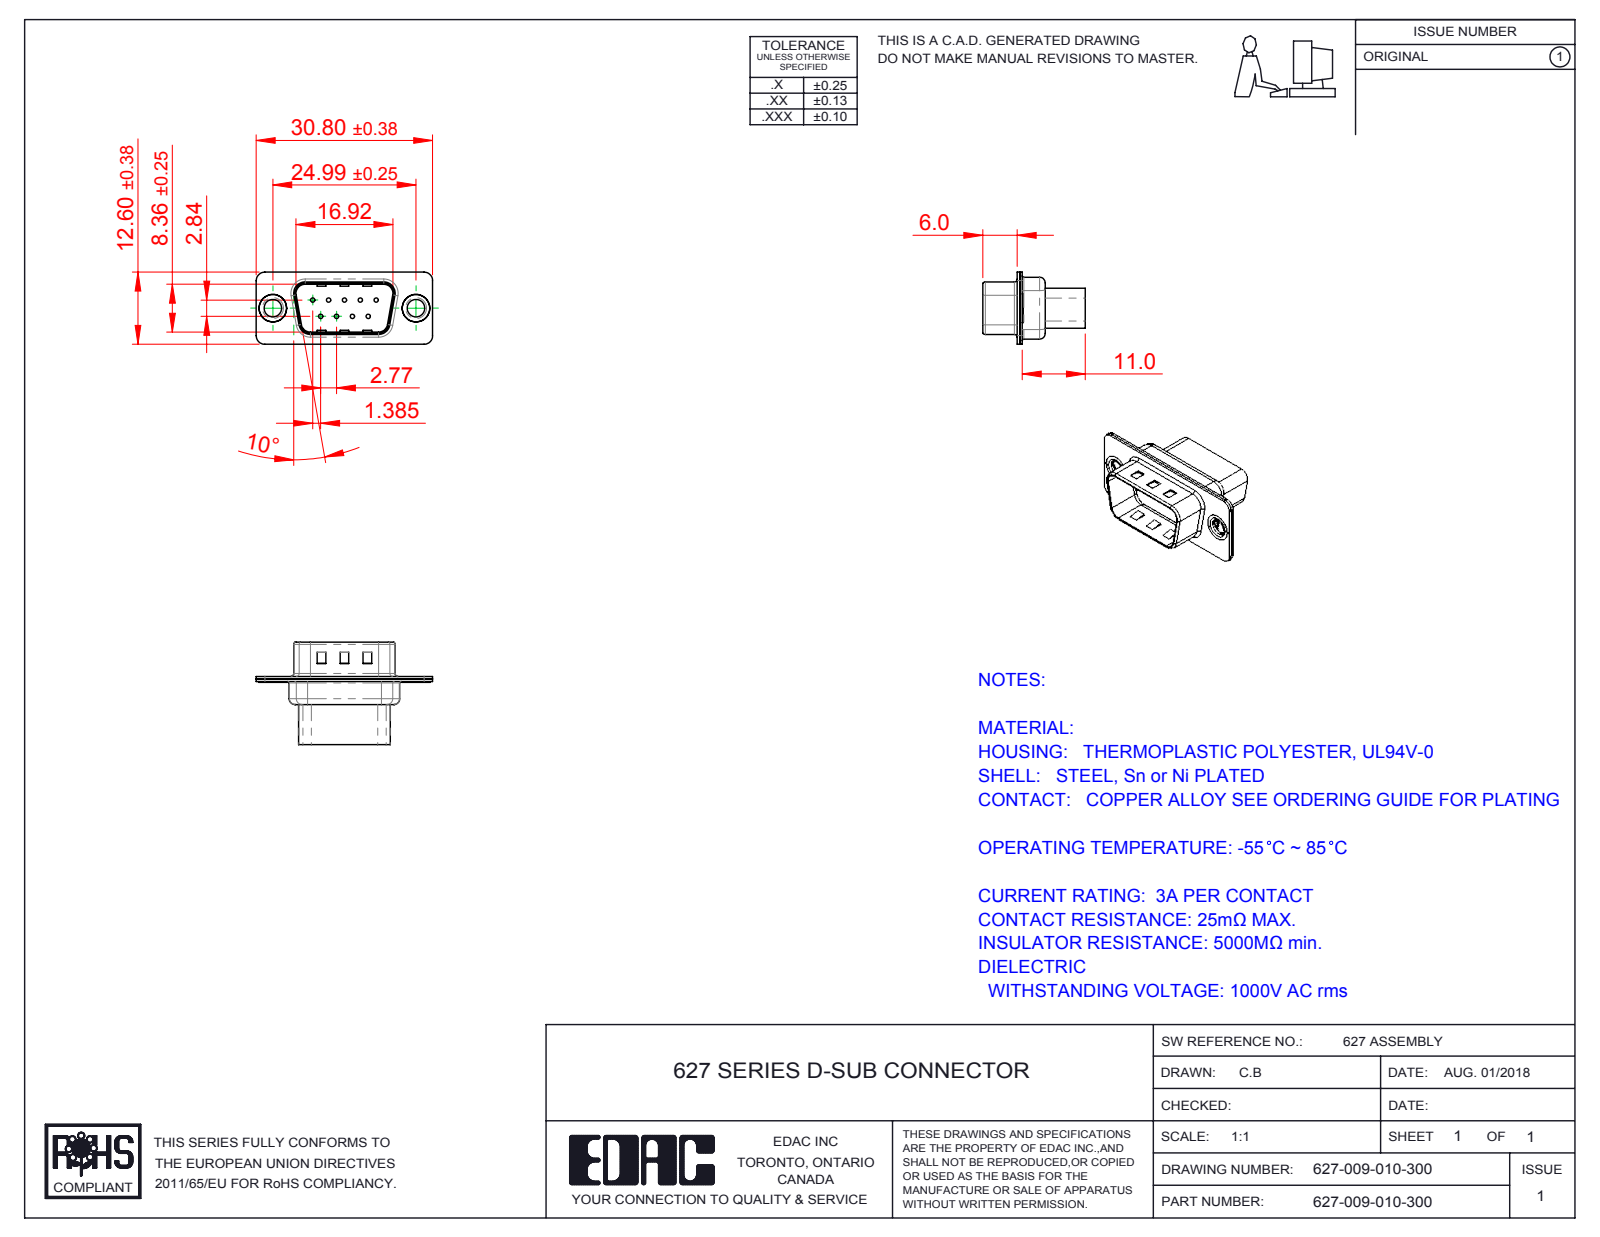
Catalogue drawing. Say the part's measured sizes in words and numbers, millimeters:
The part is named "627 Shell Front_09 Contacts; 627-009-010-300; 627 Housing_09 HP; 627 Thru Hole Rivet (+1 more)". Its 3-D file was written by "SolidWorks 2016 (CONFIG_CONTROL_DESIGN)". It is 5 solids with 350 faces: 125 planar, 167 cylindrical and 58 other. Overall it measures 30.8 by 17.9 by 12.6 millimeters. Its volume is 1 632 cubic millimeters and its surface area 3 461 square millimeters. Round holes: 9 of diameter 0.75, 9 of diameter 1.6, 9 of diameter 2, 2 of diameter 3.05, 2 of diameter 4, 2 of diameter 4.8. Round bosses or shafts: 2 of diameter 5, 2 of diameter 4.9, 2 of diameter 3.55. Partial cylindrical surfaces (rounded edges, fillets, slot ends): 18 of radius 1.5, 12 of radius 2, 8 of radius 0.5, 8 of radius 1.6, 4 of radius 0.25, 4 of radius 0.6, 4 of radius 0.65, 4 of radius 0.9. The main face-to-face distances are 0.45, 0.4, 0.9, 0.82, 9.58, 1.4, 0.68, 7.68, 1.08, 8.08. The hole center spacings are 3.16, 2.77, 5.54, 5.03, 5.04, 8.31, 7.48, 7.49.
